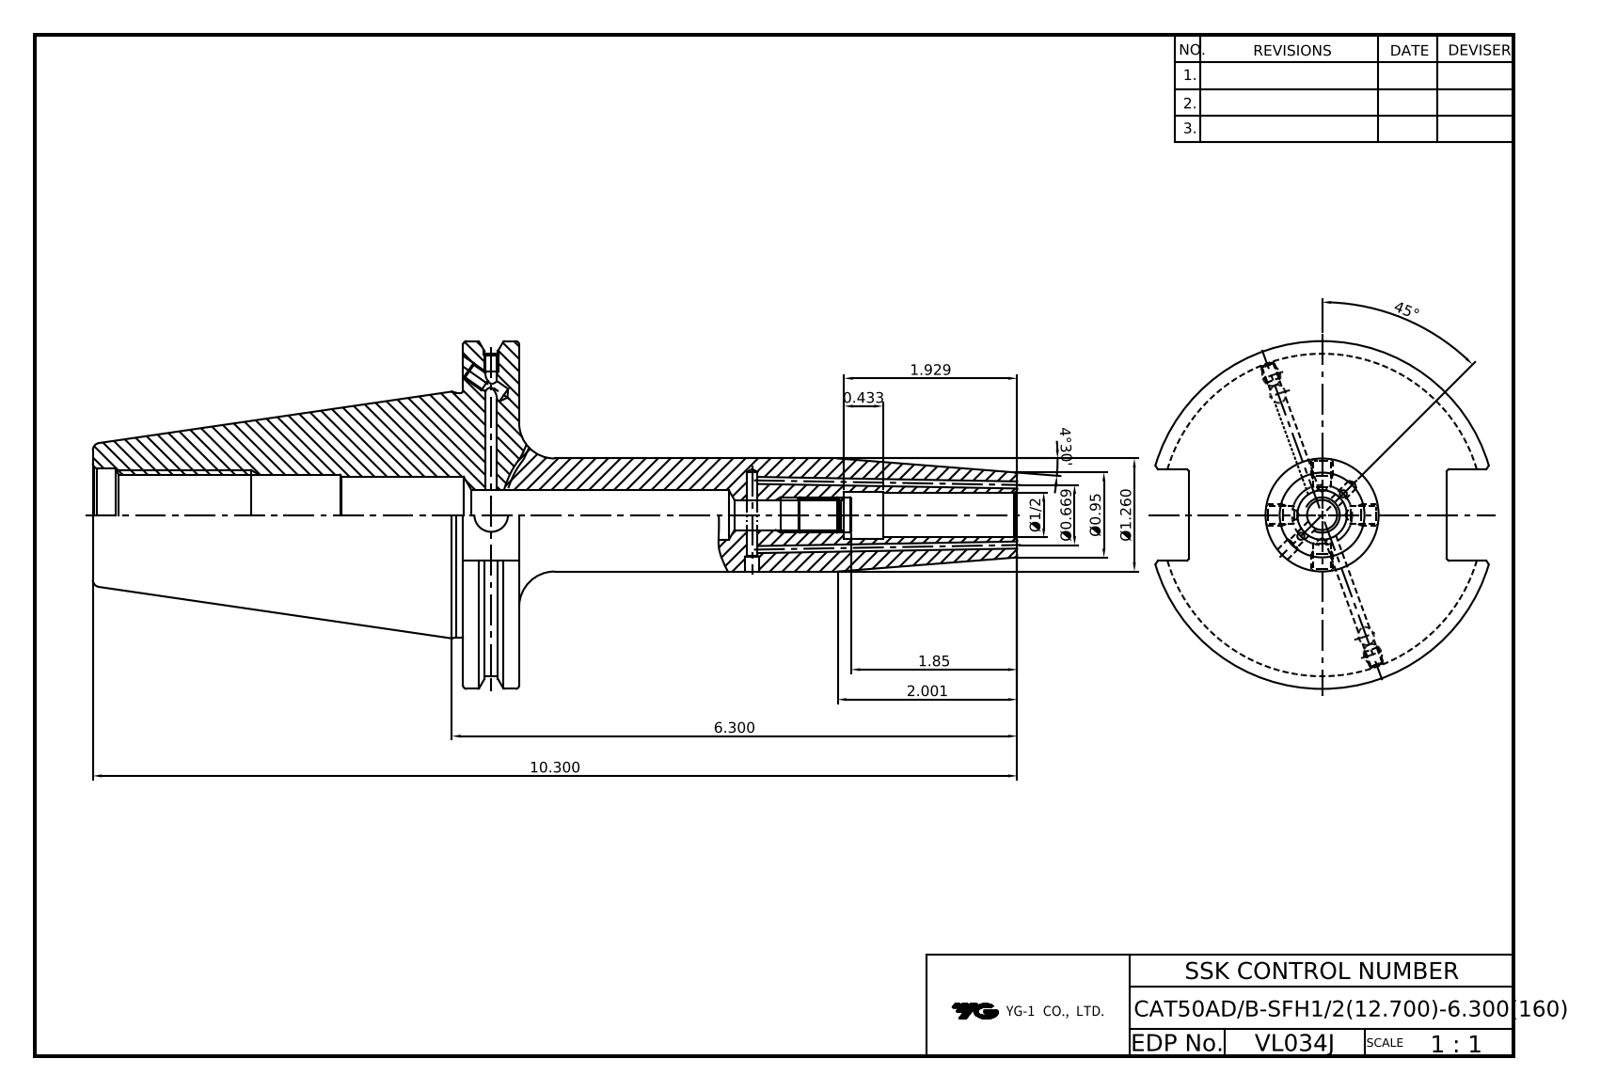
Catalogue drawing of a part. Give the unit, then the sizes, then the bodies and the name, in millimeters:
Units: millimetres
Overall size (bounding box): 261.6 × 98.42 × 94.69
Round holes (diameter × count): ⌀2 ×2, ⌀3.24 ×2, ⌀4.13 ×2, ⌀4.2 ×2, ⌀5 ×2, ⌀8.92 ×1, ⌀9.53 ×1, ⌀12.7 ×1, ⌀13.9 ×1, ⌀14 ×1, ⌀21.5 ×1, ⌀21.97 ×1
Round bosses / shafts (diameter × count): ⌀98.42 ×1, ⌀91.29 ×1, ⌀69.25 ×1, ⌀32 ×1
Main face-to-face distances: 15.88, 104.77, 120.65, 73.03, 25.9, 261.6, 156.83, 140.95, 110.82, 6.05
Volume: 410 112 mm³ · Surface area: 63 697 mm²
Bodies: 1 solid, 92 faces (37 planar, 30 cylindrical, 25 other)
Part name (STEP PRODUCT): LO-CAT50ADB-SFH12.7C-160
STEP written by: Autodesk Inventor 2022 (AUTOMOTIVE_DESIGN)
